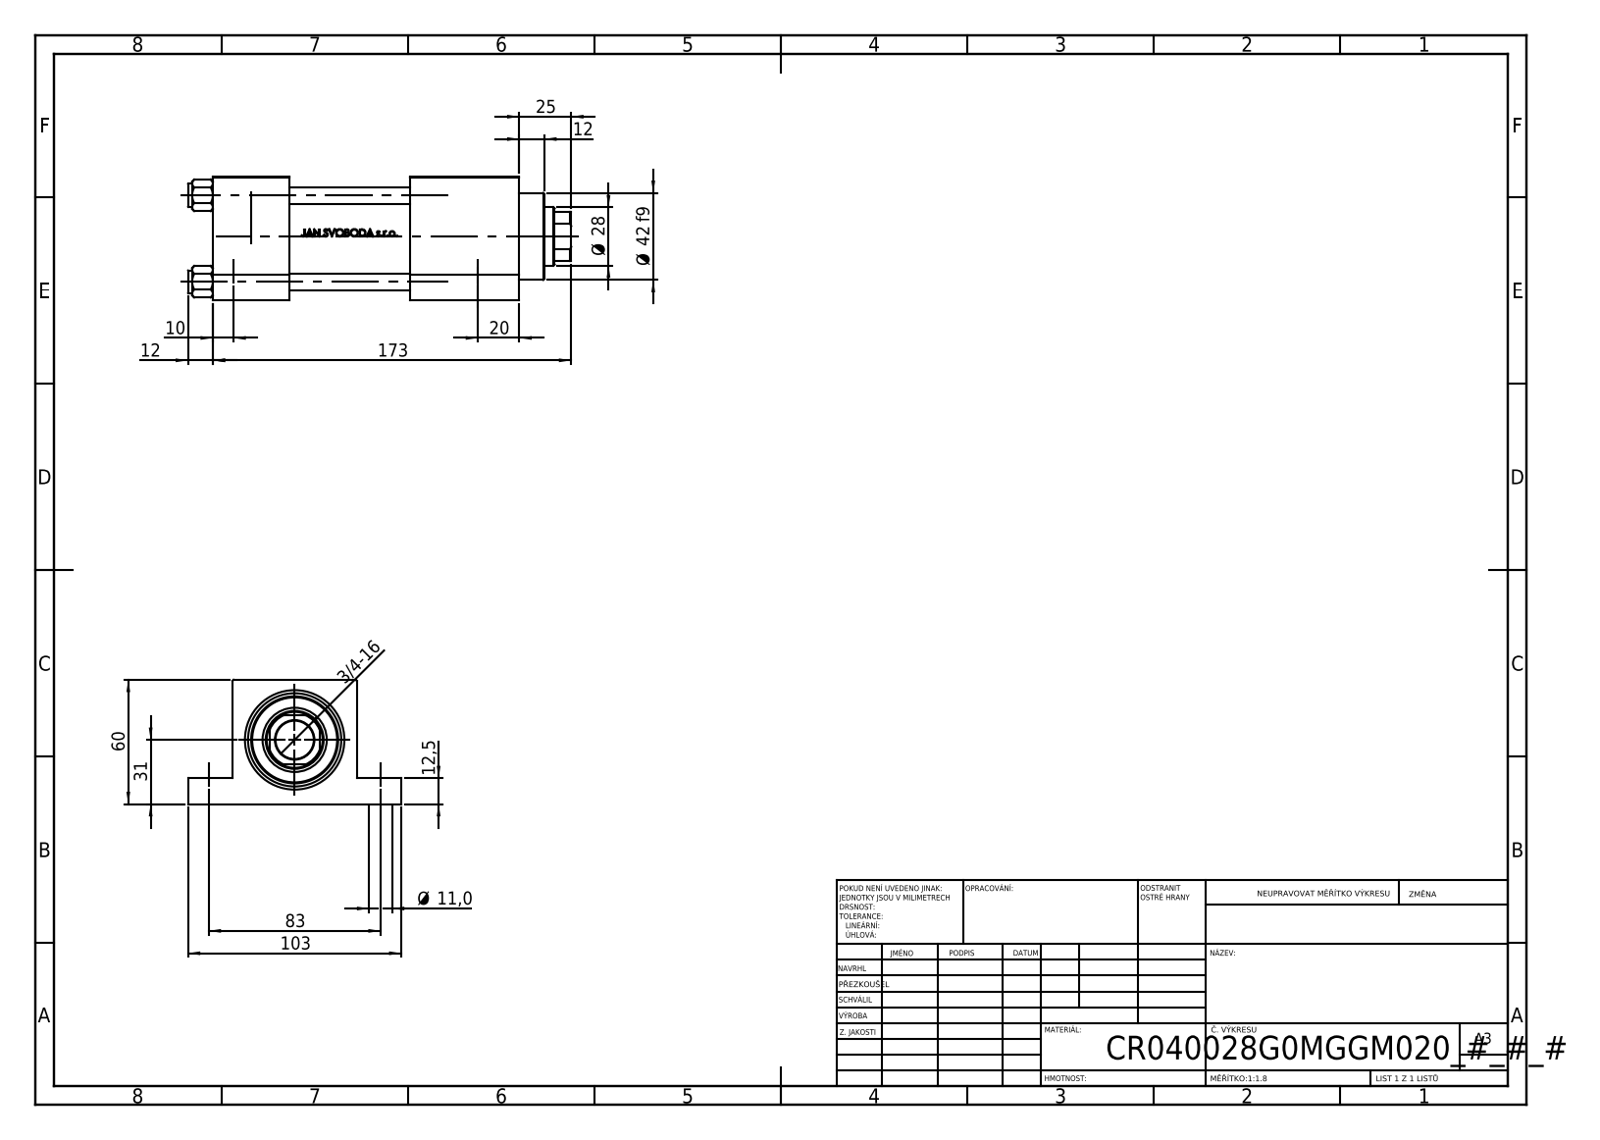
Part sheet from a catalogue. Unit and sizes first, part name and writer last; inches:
Units: inches
Overall size (bounding box): 7.283 × 4.055 × 2.362
Round holes (diameter × count): ⌀0.315 ×4, ⌀0.433 ×4, ⌀0.276 ×2, ⌀0.656 ×2, ⌀0.945 ×2, ⌀0.728 ×1, ⌀1.102 ×1, ⌀1.22 ×1, ⌀1.575 ×1, ⌀1.772 ×1
Round bosses / shafts (diameter × count): ⌀0.433 ×4, ⌀1.811 ×1, ⌀1.654 ×1
Partial cylindrical surfaces — rounded edges, fillets, slot ends (radius × count): R0.531 ×1
Main face-to-face distances: 2.362, 1.457, 0.492, 1.87, 3.74, 2.283, 5.827, 4.37, 2.087, 0.846
Hole centre spacings: 1.642, 1.133, 1.189, 1.668, 1.766, 2.322, 3.268, 4.299
Volume: 28.81 in³ · Surface area: 186.3 in²
Bodies: 11 solids, 1090 faces (432 planar, 126 cylindrical, 532 other)
Part name (STEP PRODUCT): V215CR_G_TYCINKA; V215_VC_A; NUT_M5_G; V215CR_VCP_G (+1 more)
STEP written by: SolidWorks 2019 (CONFIG_CONTROL_DESIGN)
